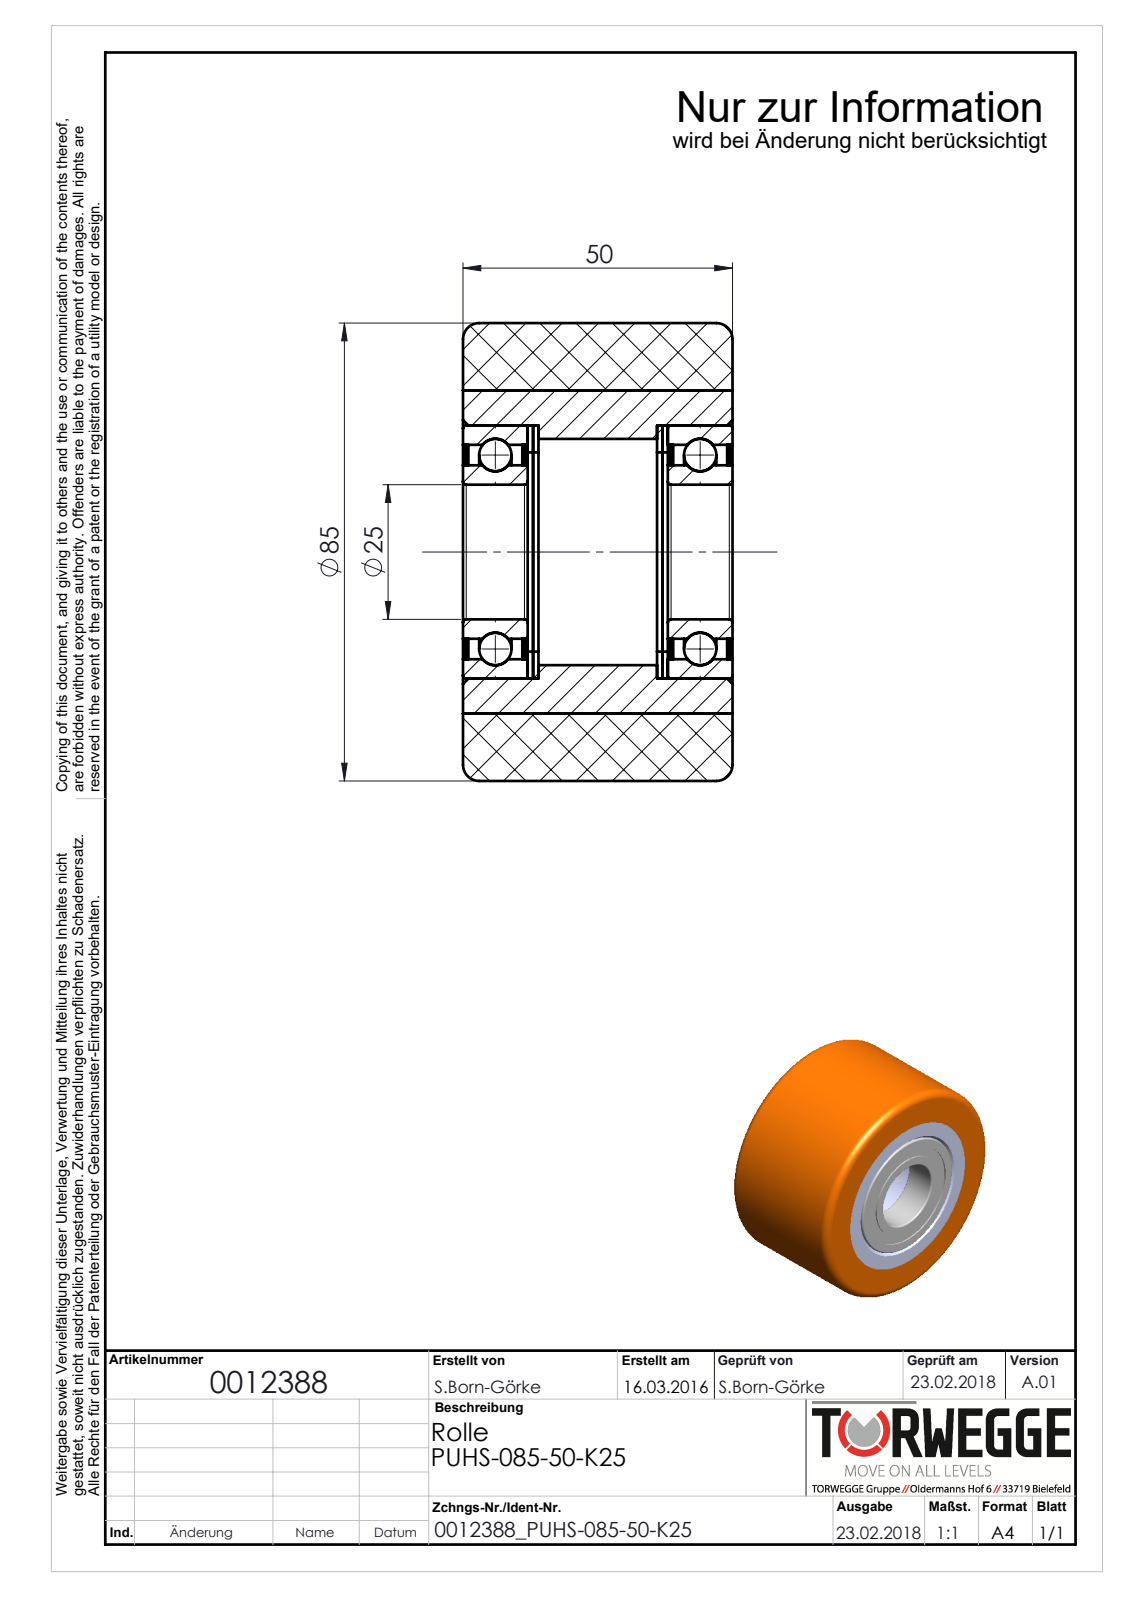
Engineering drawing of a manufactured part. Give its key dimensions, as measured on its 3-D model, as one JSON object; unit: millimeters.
{"part_name": "0012388_PUHS-085-50-K25", "step_written_by": "SolidWorks 2016 (AUTOMOTIVE_DESIGN)", "units": "millimeters", "bodies": {"solids": 16, "faces": 158, "planar": 30, "cylindrical": 68, "other": 60}, "overall_size": [85, 85, 50], "volume_mm3": 230990, "surface_area_mm2": 75520, "round_holes": [[25, 1], [32.2, 1], [37, 1], [39.8, 1], [42, 1], [60, 1]], "round_bosses_or_shafts": [[85, 1], [47, 1]], "face_to_face_distances": [1, 38, 50, 12, 0.5, 13, 37, 25, 24, 36]}
